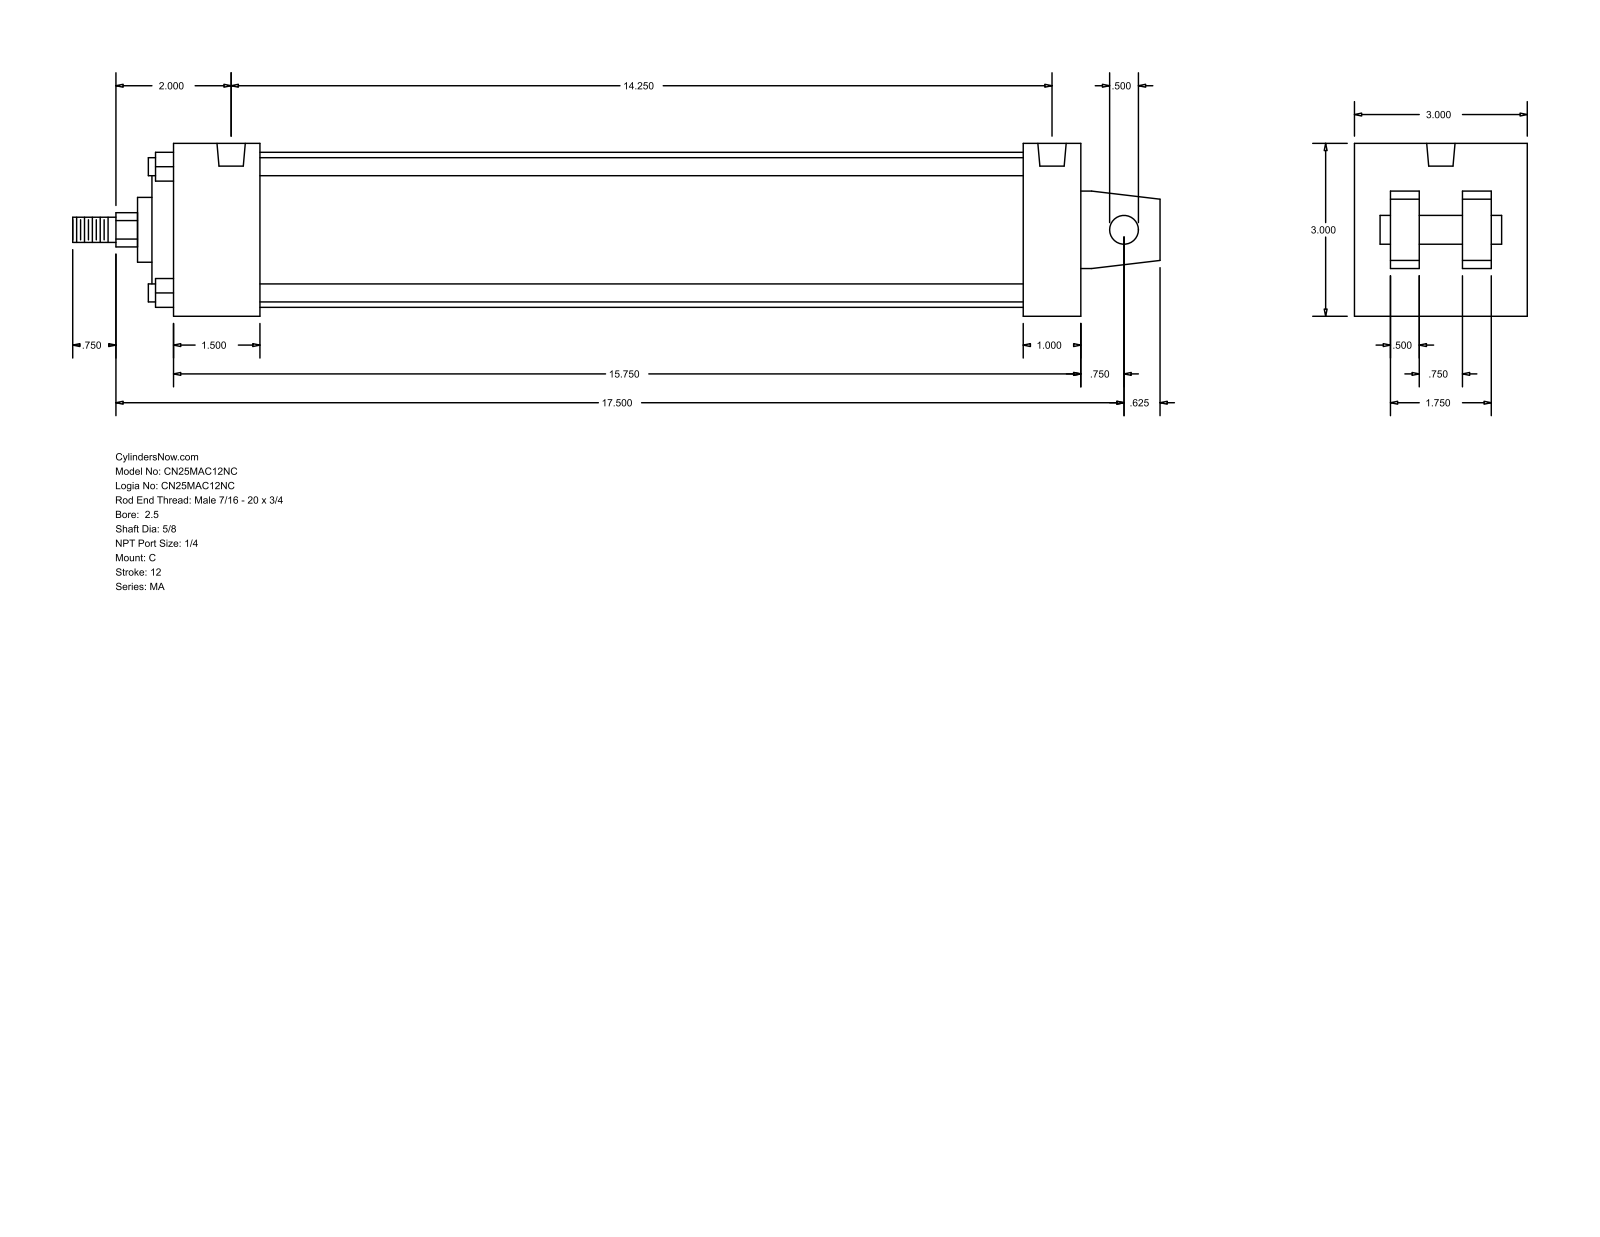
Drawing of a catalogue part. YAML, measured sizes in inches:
part_name: "MA_C__0250_0.625"
step_written_by: "GSSL Pune (CONFIG_CONTROL_DESIGN)"
units: inches
bodies: {solids: 0, faces: 105, planar: 77, cylindrical: 28, other: 0}
overall_size: [18.875, 3, 3]
round_holes:
  - {diameter: 0.313, count: 4}
  - {diameter: 0.492, count: 2}
round_bosses_or_shafts:
  - {diameter: 0.313, count: 4}
  - {diameter: 2.69, count: 1}
  - {diameter: 2, count: 1}
  - {diameter: 1.125, count: 1}
  - {diameter: 0.625, count: 1}
  - {diameter: 0.5, count: 1}
  - {diameter: 0.437, count: 1}
partial_cylinders:
  - {radius: 0.297, count: 1}
face_to_face_distances: [3, 15.75, 0.5, 0.625, 2.375, 1.875, 1, 1.5, 14.75, 13.25]
hole_center_spacings: [14.25]
